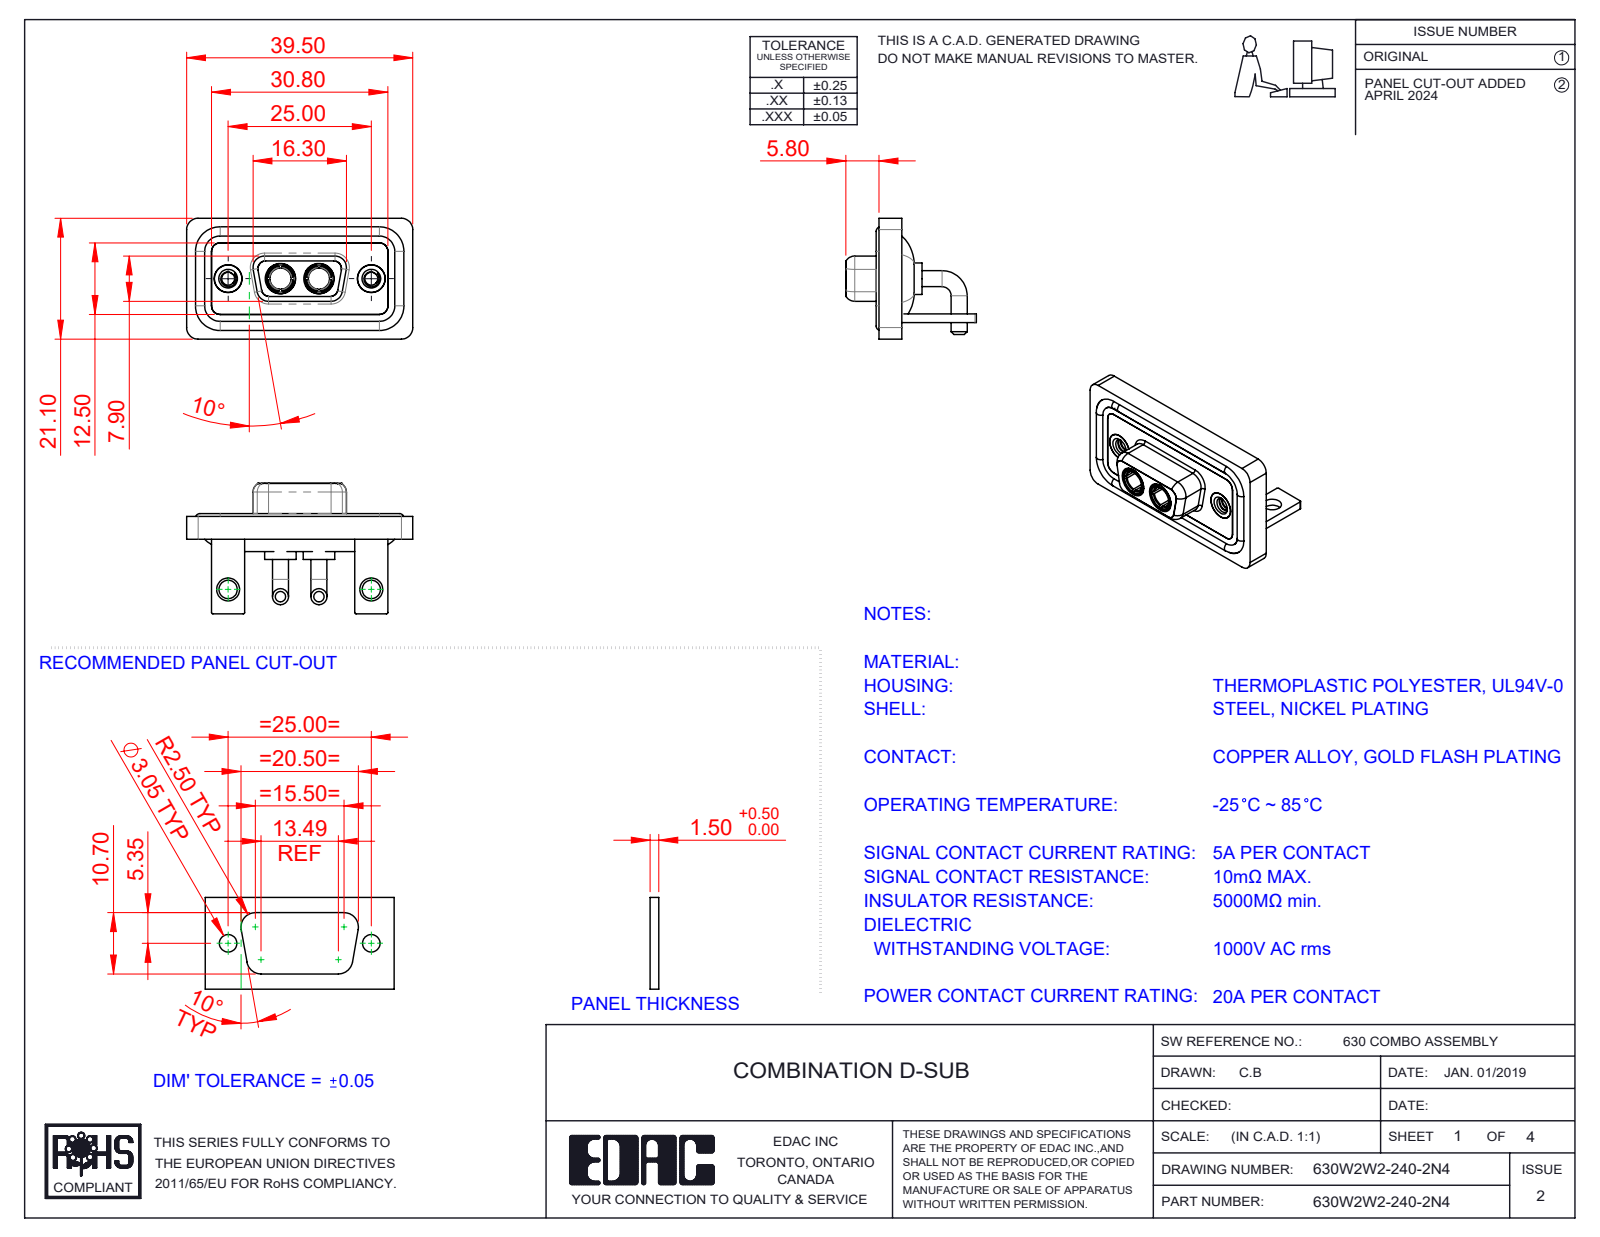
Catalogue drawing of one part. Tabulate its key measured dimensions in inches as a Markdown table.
| quantity | value |
| --- | --- |
| part name | 630Combo Waterproof Housing_09 Contacts; 630Combo Threaded Rivet_2; Power Socket_20A RA; 630Combo Housing_2W2 (+4 more) |
| STEP written by | SolidWorks 2023 (CONFIG_CONTROL_DESIGN) |
| units | inches |
| bodies | 13 solids, 590 faces (183 planar, 262 cylindrical, 145 other) |
| overall size | 1.555 × 0.898 × 0.831 |
| volume | 0.316 in³ |
| surface area | 13.21 in² |
| round holes (diameter × count) | 0.191 × 4, 0.089 × 2, 0.126 × 2, 0.146 × 2, 0.157 × 2, 0.159 × 2, 0.197 × 2, 0.209 × 2 |
| round bosses / shafts (diameter × count) | 0.11 × 4, 0.063 × 4, 0.217 × 2, 0.205 × 2, 0.195 × 2, 0.195 × 2, 0.189 × 2, 0.187 × 2 |
| partial cylindrical surfaces (radius × count) | 0.079 × 19, 0.059 × 18, 0.01 × 16, 0.053 × 8, 0.063 × 8, 0.02 × 5, 0.024 × 4, 0.026 × 4 |
| main face-to-face distances | 0.016, 0.114, 0.059, 0.071, 0.043, 0.146, 0.031, 0.098, 0.063, 0.122 |
| hole center spacings | 0.36, 0.624, 0.984, 0.265 |
